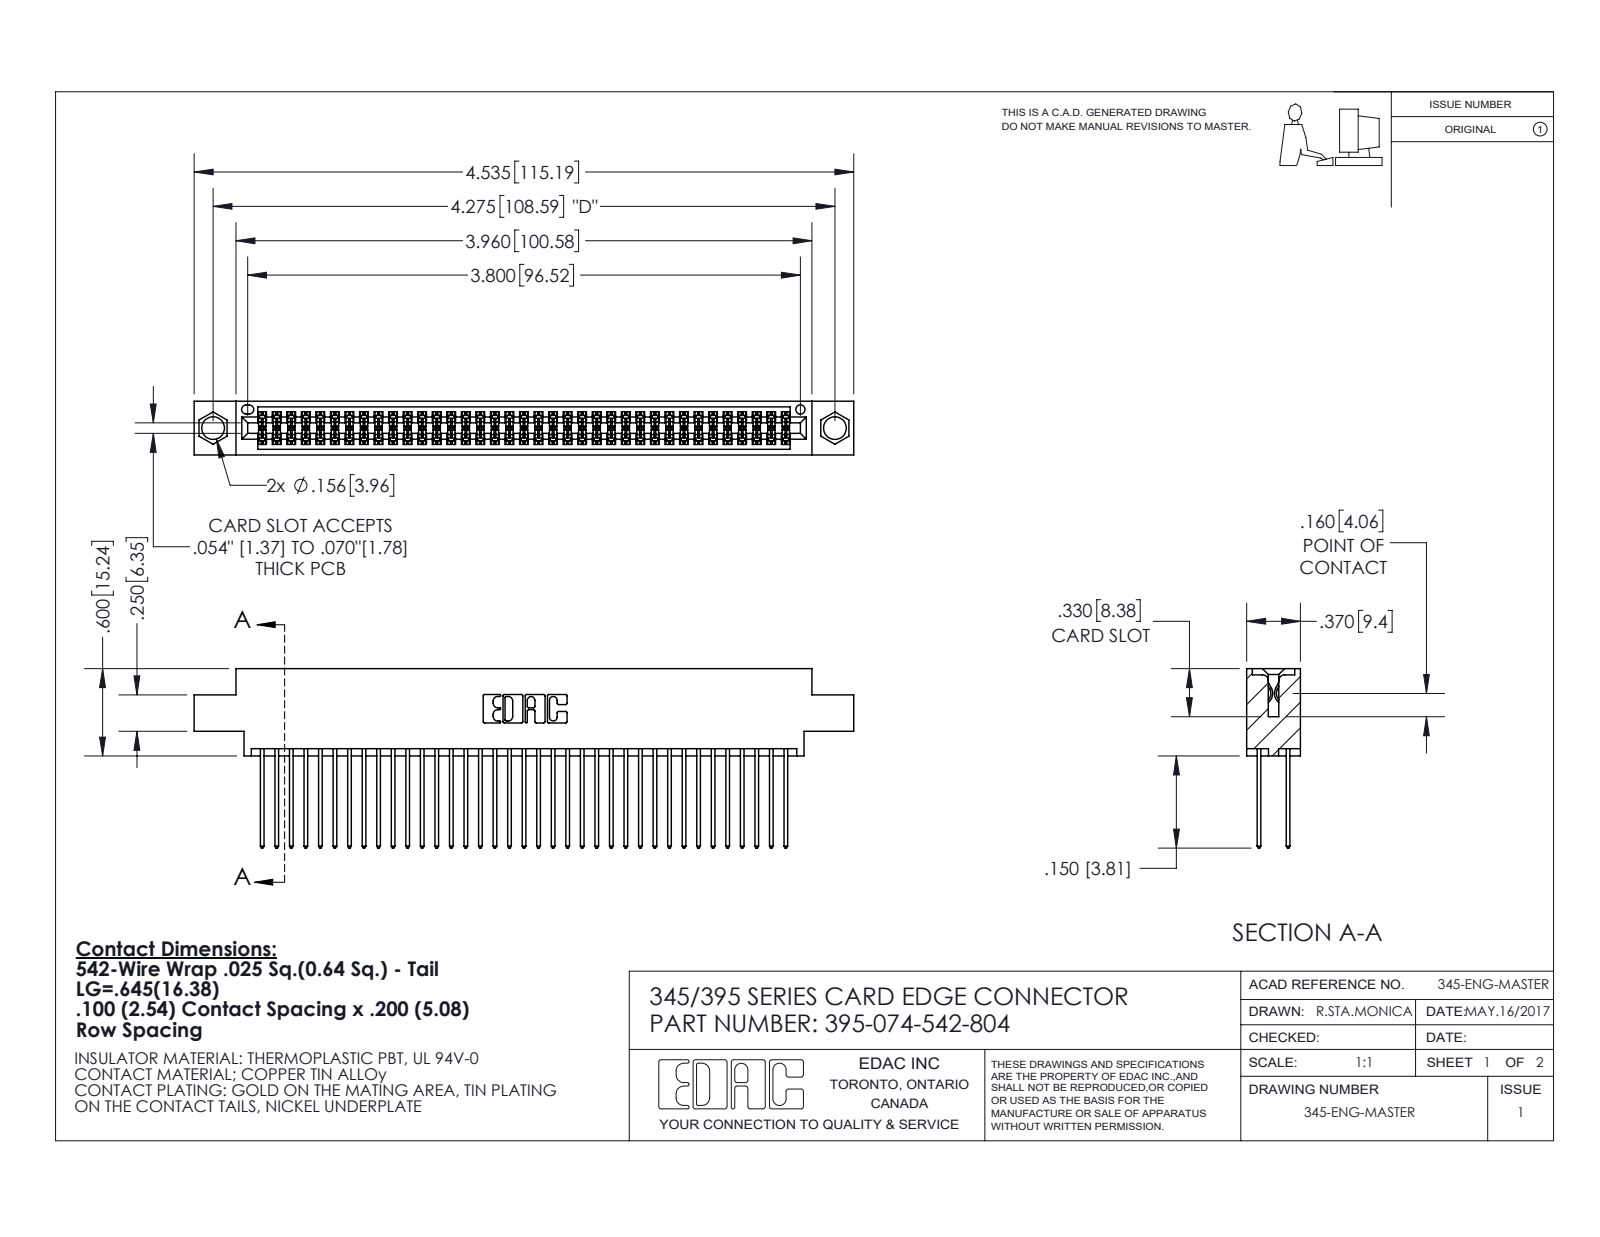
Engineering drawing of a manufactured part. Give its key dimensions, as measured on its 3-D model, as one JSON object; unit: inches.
{"part_name": "345 Part_0.170 Offset - 0.156 Dia-TI; 395-074-542-804; 345-292-001_345-293-142", "step_written_by": "SolidWorks 2020 (CONFIG_CONTROL_DESIGN)", "units": "inches", "bodies": {"solids": 75, "faces": 3844, "planar": 2540, "cylindrical": 1304, "other": 0}, "overall_size": [4.535, 1.232, 0.37], "volume_in3": 0.688, "surface_area_in2": 28.16, "round_holes": [[0.156, 2], [0.064, 1]], "partial_cylinders_radius": [[0.006, 148], [0.01, 74], [0.01, 22], [0.007, 6], [0.031, 6], [0.026, 3], [0.014, 2], [0.019, 2]], "face_to_face_distances": [0.072, 0.298, 0.2, 0.098, 0.272, 0.025, 0.37, 0.225, 0.175, 0.149], "hole_center_spacings": [0.27, 4.039, 4.275]}
